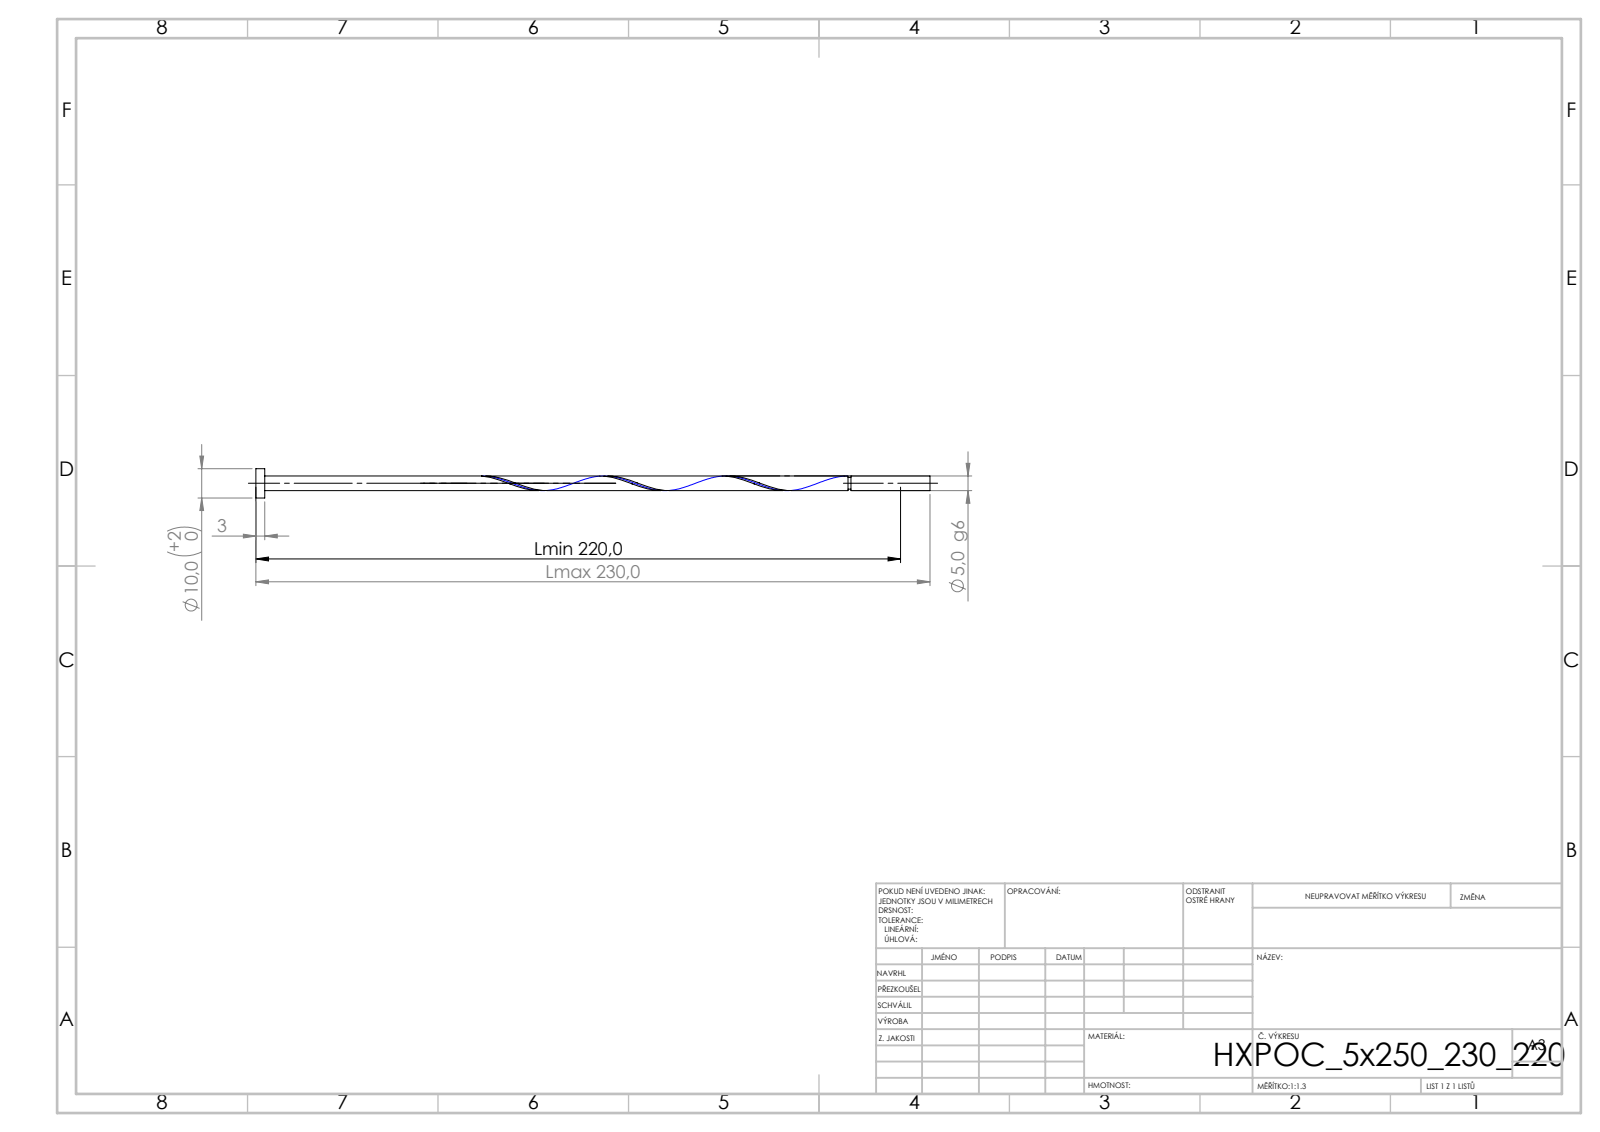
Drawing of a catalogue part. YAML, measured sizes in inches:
step_written_by: "SolidWorks 2019 (CONFIG_CONTROL_DESIGN)"
units: inches
bodies: {solids: 1, faces: 21, planar: 6, cylindrical: 14, other: 1}
overall_size: [9.055, 0.394, 0.394]
volume: 0.283
surface_area: 6.034
round_bosses_or_shafts:
  - {diameter: 0.394, count: 1}
  - {diameter: 0.197, count: 1}
  - {diameter: 0.157, count: 1}
face_to_face_distances: [0.118, 9.055, 8.937, 7.994, 7.876, 1.061, 7.955, 7.837, 0.039, 1.1]
